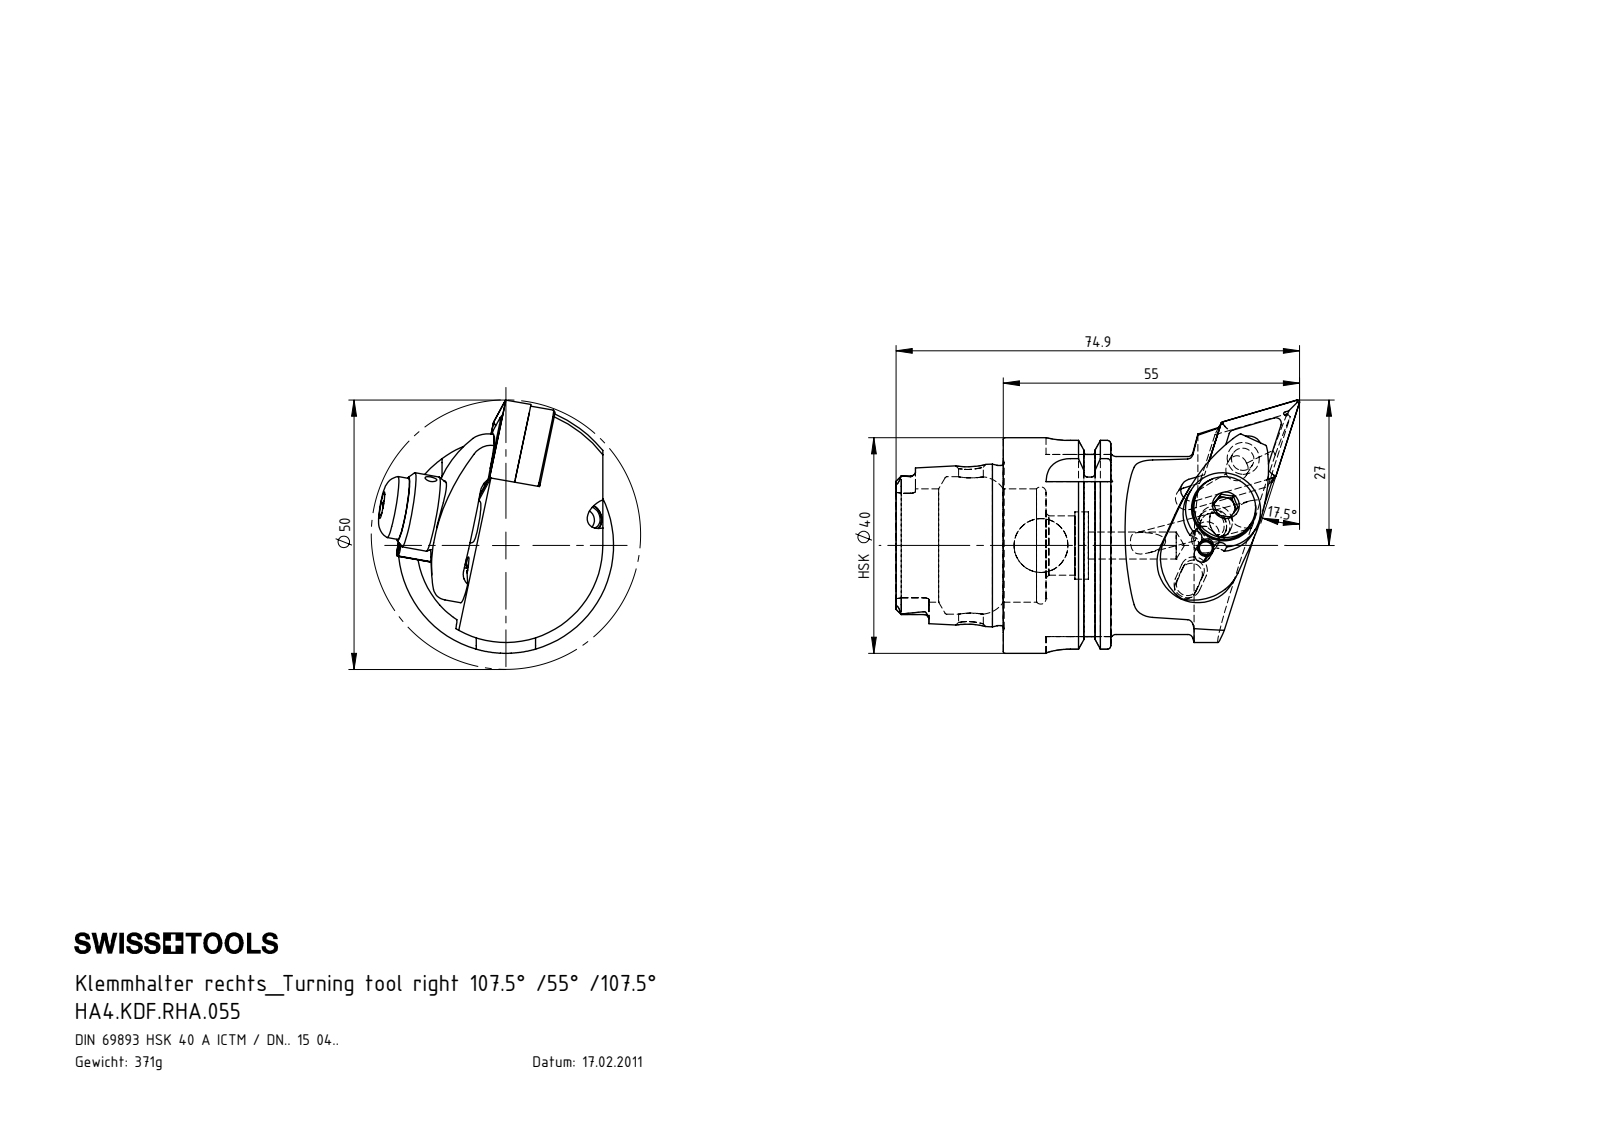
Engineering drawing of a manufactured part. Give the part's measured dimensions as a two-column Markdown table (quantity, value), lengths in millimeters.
| quantity | value |
| --- | --- |
| part name | WCC-ER4.103.032_A; WCC-ER3.102.024_C; WCC-ER5.102.005_A; WCC-ER2.001.010_A (+7 more) |
| STEP written by | SolidWorks 2022 (AUTOMOTIVE_DESIGN) |
| units | millimeters |
| bodies | 11 solids, 465 faces (122 planar, 154 cylindrical, 189 other) |
| overall size | 74.9 × 47 × 43.63 |
| volume | 46 482 mm³ |
| surface area | 19 019 mm² |
| round holes (diameter × count) | 2 × 3, 5 × 3, 4.2 × 2, 7 × 2, 2.4 × 1, 3 × 1, 4 × 1, 4.6 × 1, 5.16 × 1, 6.2 × 1, 6.5 × 1, 8.5 × 1 |
| round bosses / shafts (diameter × count) | 5 × 2, 3 × 2, 40 × 1, 34.75 × 1, 33 × 1, 29.71 × 1, 14 × 1, 11.5 × 1 |
| partial cylindrical surfaces (radius × count) | 0.39 × 6, 0.69 × 6, 0.9 × 6, 0.4 × 4, 4.5 × 4, 1.5 × 3, 3 × 3, 1.82 × 2 |
| main face-to-face distances | 6.02, 12.7, 12.3, 7.95, 1.31, 7.33, 12, 9.2, 19.95, 3.17 |
| hole center spacings | 23, 14.81, 14.99, 23.01, 7.99, 8, 8.01, 8.02 |
